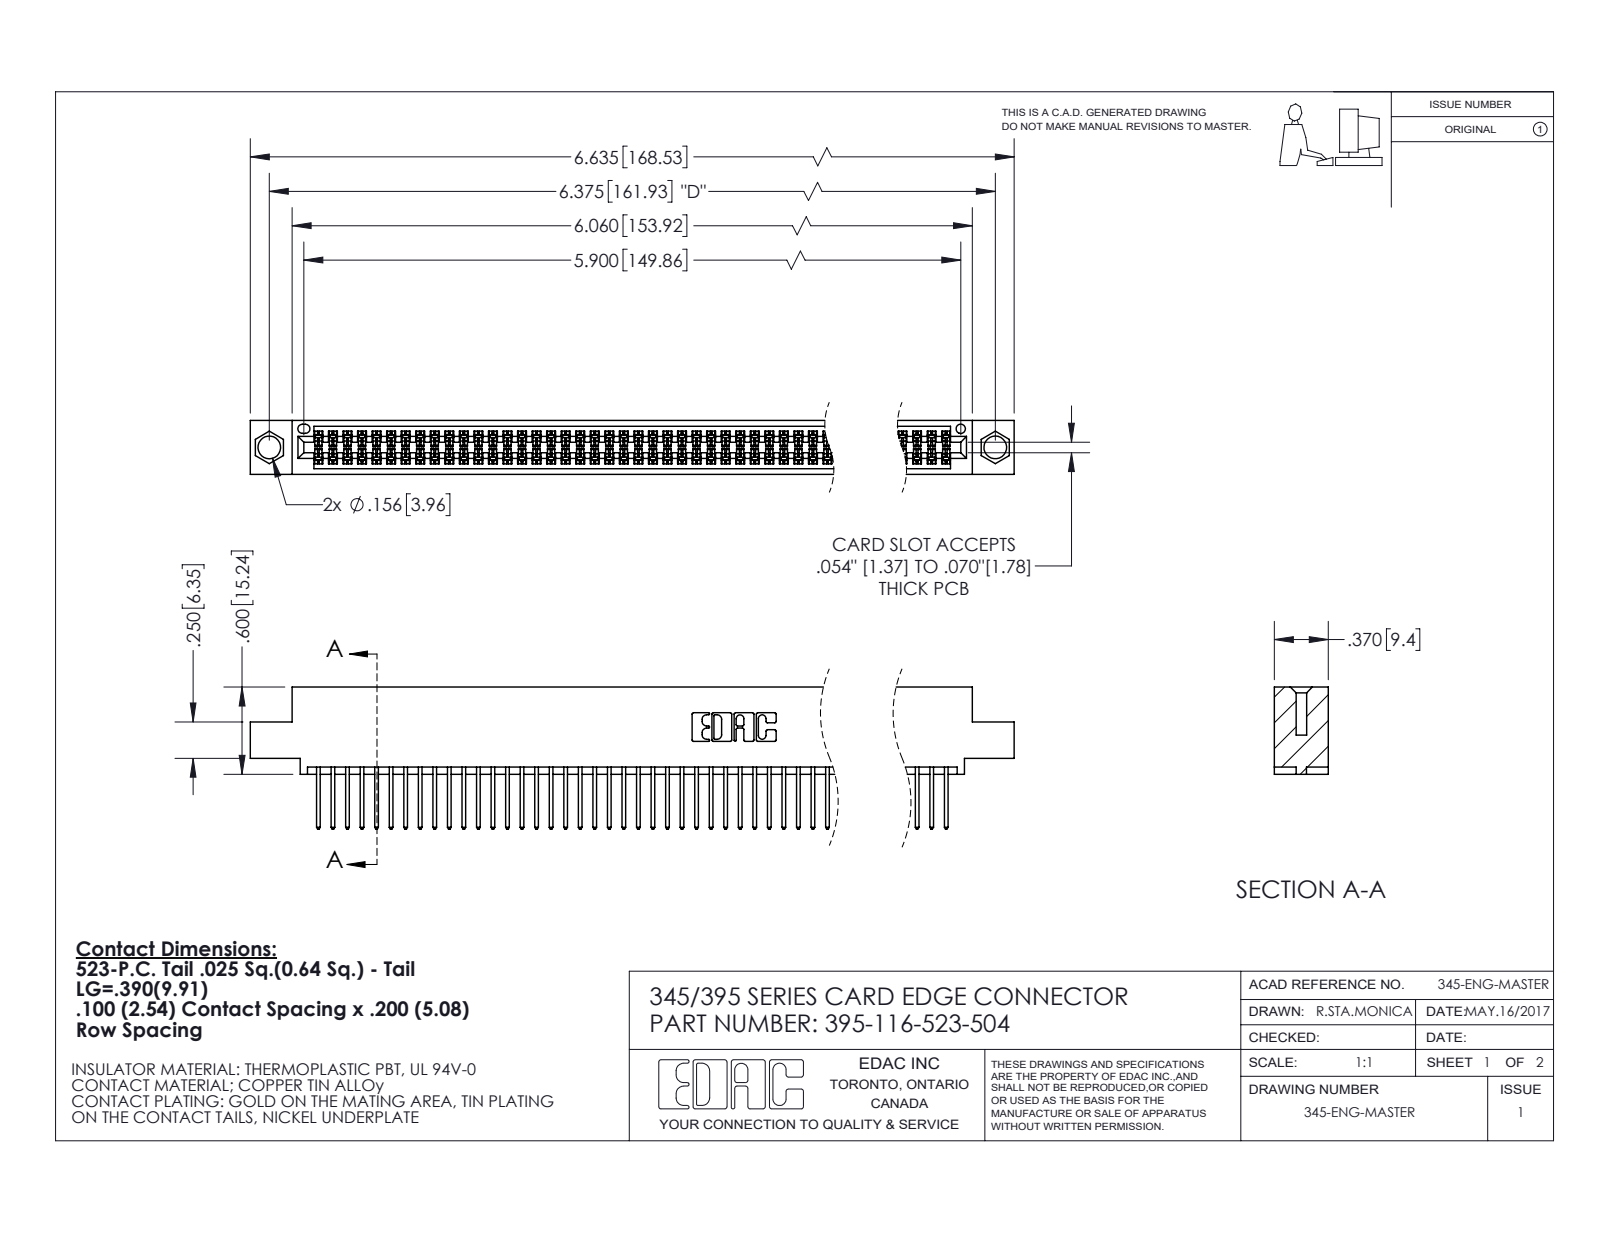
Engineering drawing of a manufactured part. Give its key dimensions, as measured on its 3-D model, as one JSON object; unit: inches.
{"part_name": "395-116-523-504; 345 Part_0.110 Offset - 0.156 Dia-TI; 345-292-001_345-293-123", "step_written_by": "SolidWorks 2020 (CONFIG_CONTROL_DESIGN)", "units": "inches", "bodies": {"solids": 117, "faces": 5944, "planar": 3926, "cylindrical": 2018, "other": 0}, "overall_size": [6.635, 0.977, 0.37], "volume_in3": 1.012, "surface_area_in2": 40.03, "round_holes": [[0.156, 2], [0.064, 1]], "partial_cylinders_radius": [[0.006, 175], [0.01, 116], [0.01, 22], [0.007, 6], [0.031, 6], [0.026, 3], [0.014, 2], [0.019, 2]], "face_to_face_distances": [0.298, 0.072, 0.2, 0.098, 0.272, 0.025, 0.37, 0.225, 0.175, 0.149], "hole_center_spacings": [0.27, 6.139, 6.375]}
